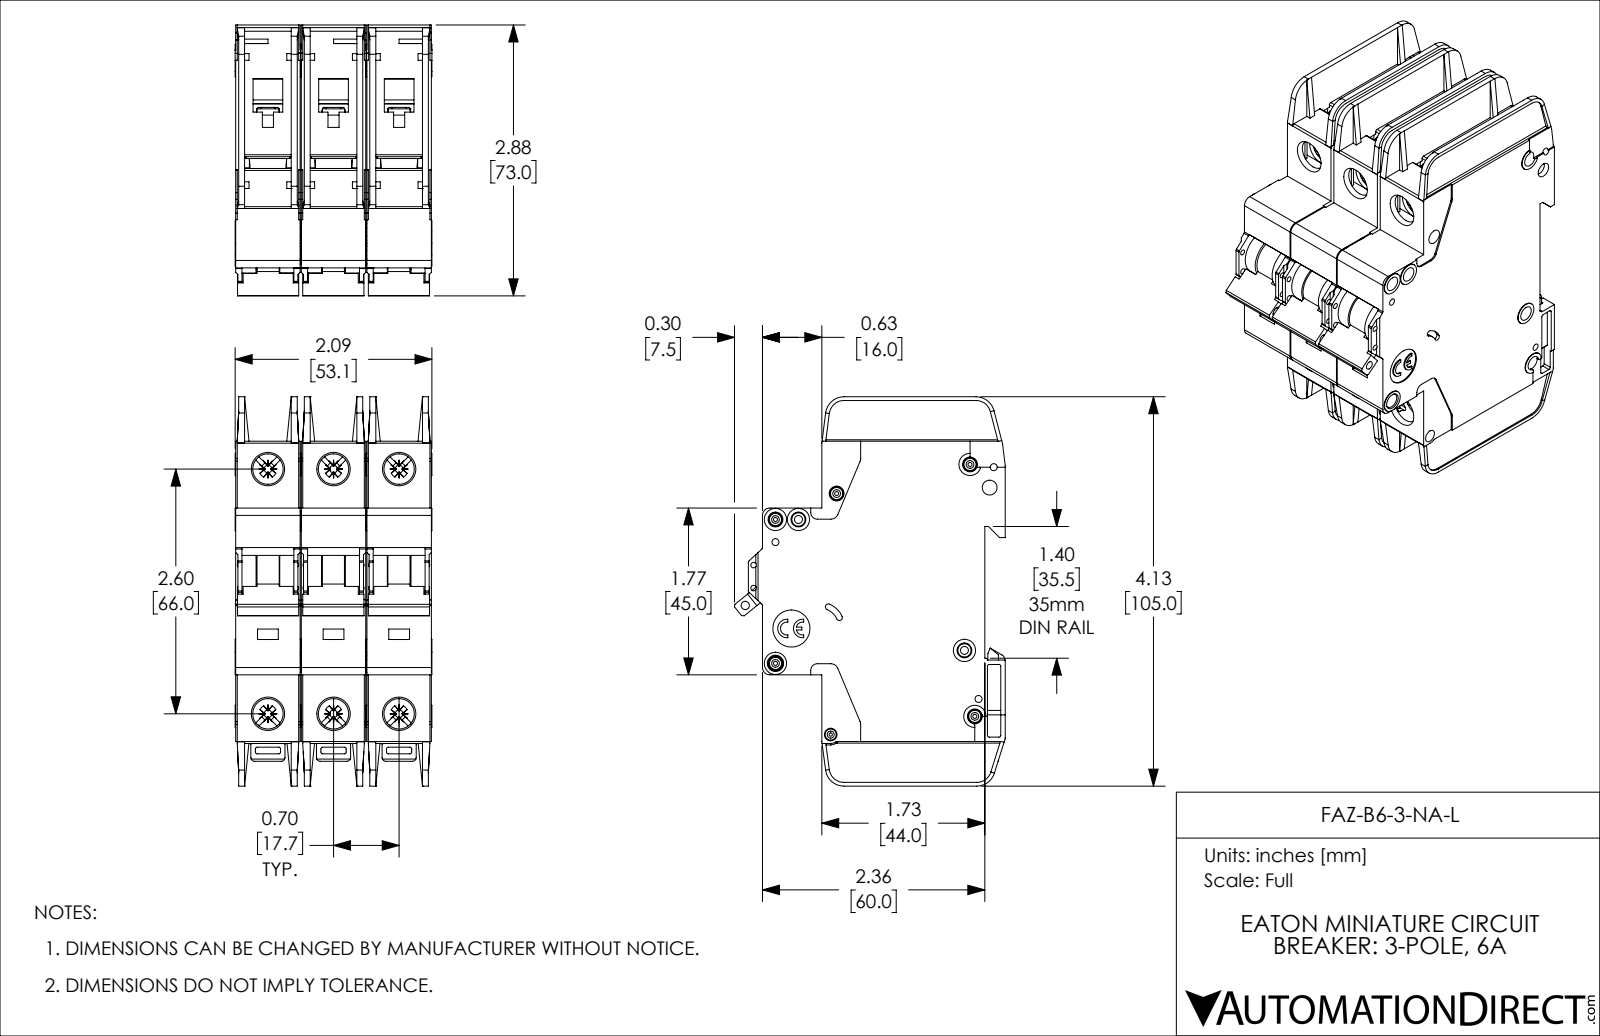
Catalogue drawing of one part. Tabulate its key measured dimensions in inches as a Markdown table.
| quantity | value |
| --- | --- |
| part name | FAZ-B6-3-NA-L |
| STEP written by | SolidWorks 2019 (AUTOMOTIVE_DESIGN) |
| units | inches |
| bodies | 3 solids, 3381 faces (2013 planar, 1071 cylindrical, 297 other) |
| overall size | 4.134 × 2.876 × 2.091 |
| volume | 14.05 in³ |
| surface area | 123 in² |
| round holes (diameter × count) | 0.157 × 8, 0.323 × 6, 0.043 × 5, 0.075 × 4, 0.059 × 2, 0.085 × 2, 0.035 × 1, 0.089 × 1, 0.098 × 1, 0.134 × 1, 0.394 × 1 |
| round bosses / shafts (diameter × count) | 0.13 × 5, 0.236 × 4, 0.118 × 4, 0.098 × 3 |
| partial cylindrical surfaces (radius × count) | 0.02 × 72, 0.016 × 30, 0.039 × 18, 0.043 × 12, 0.079 × 12, 0.008 × 6, 0.01 × 6, 0.028 × 6 |
| main face-to-face distances | 0.697, 0.047, 1.394, 0.685, 0.591, 1.382, 0.744, 0.65, 0.106, 0.094 |
| hole center spacings | 0.697, 2.69, 2.598, 0.244, 0.537, 0.87, 1.394, 2.948 |
